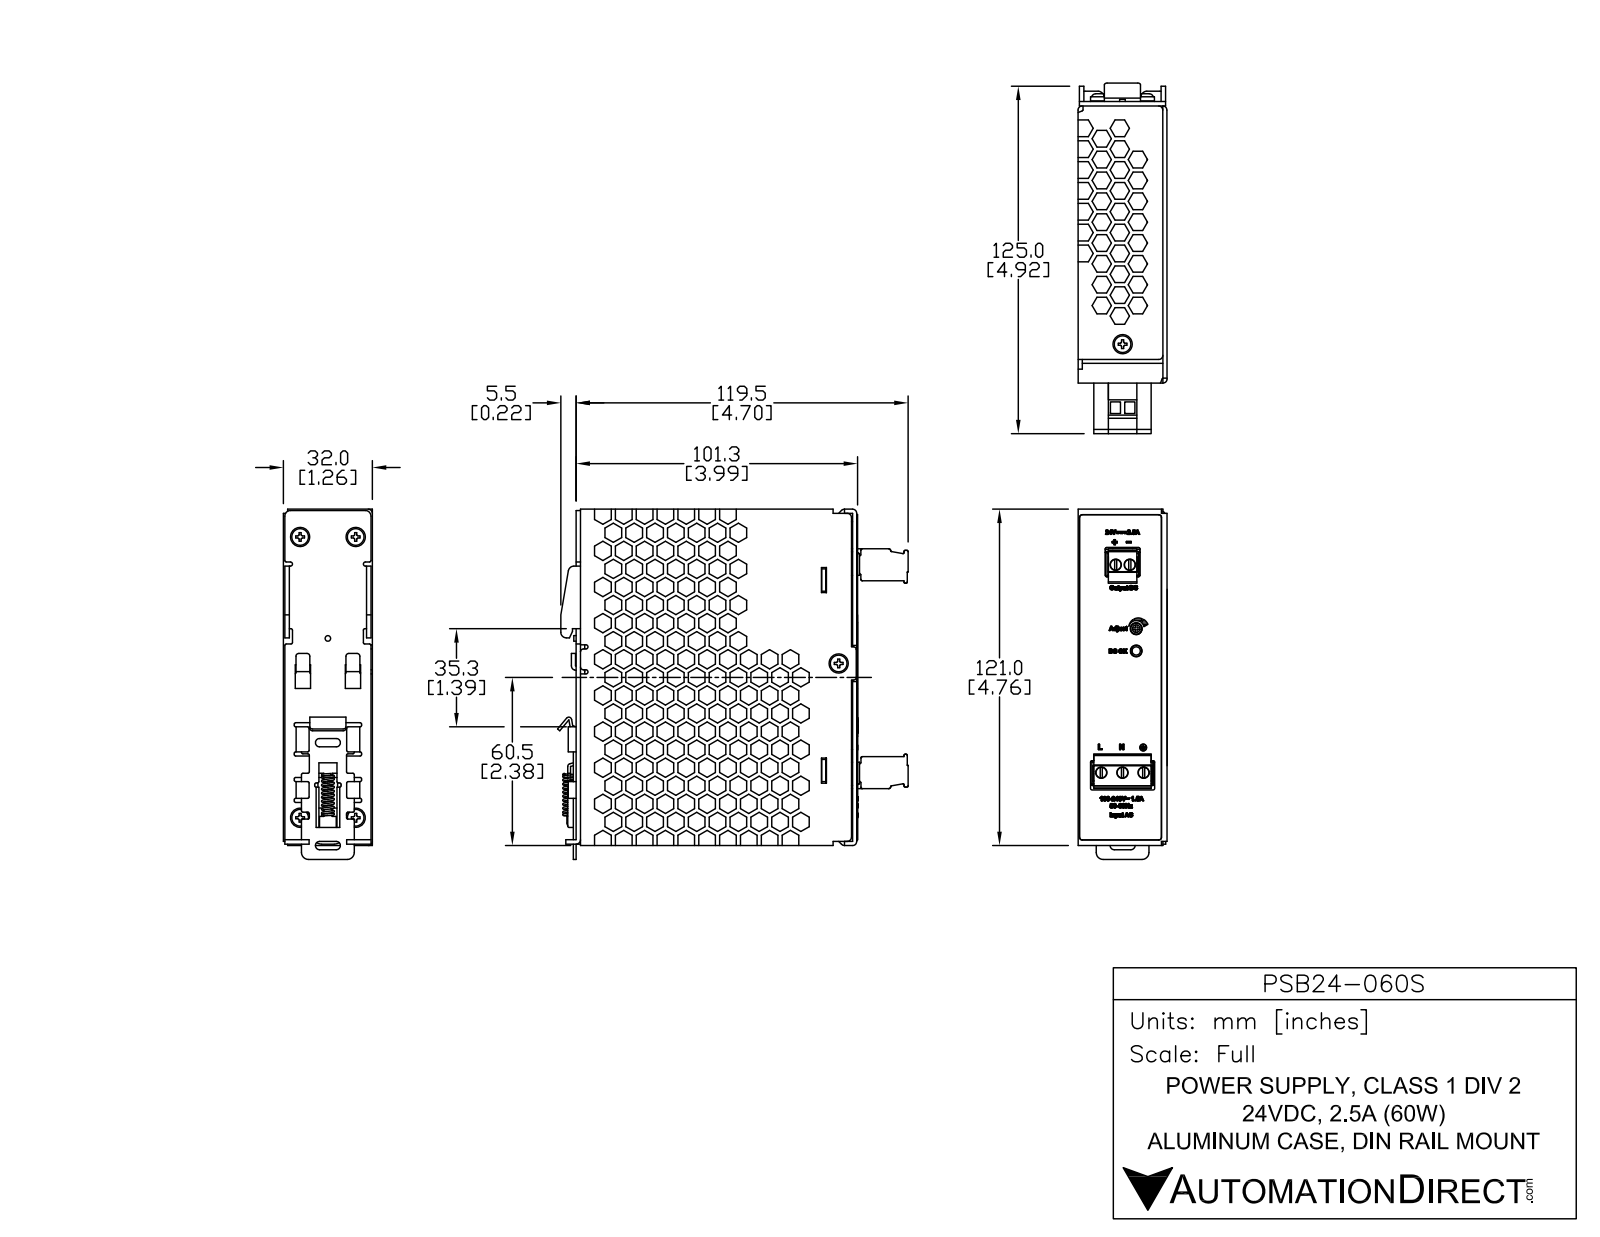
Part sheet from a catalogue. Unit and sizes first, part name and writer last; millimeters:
Units: millimetres
Overall size (bounding box): 126.2 × 126 × 32.1
Round holes (diameter × count): ⌀4 ×7, ⌀3.5 ×6, ⌀4.5 ×6, ⌀3 ×4, ⌀6 ×4, ⌀4.2 ×2, ⌀2 ×1, ⌀2.8 ×1, ⌀3.5 ×1, ⌀4.1 ×1
Round bosses / shafts (diameter × count): ⌀3 ×7, ⌀6.5 ×6, ⌀6 ×6, ⌀0.5 ×3, ⌀0.9 ×2, ⌀2.3 ×1
Partial cylindrical surfaces — rounded edges, fillets, slot ends (radius × count): R0.5 ×117, R1 ×33, R1.5 ×30, R0.1 ×14, R0.8 ×14, R2 ×10, R1.6 ×9, R0.2 ×8
Main face-to-face distances: 1.5, 1.6, 30.5, 5.6, 7.1, 4, 5.5, 24.9, 26.5, 32
Hole centre spacings: 7.6, 20, 37.8, 65.3, 74.8, 79.3, 101, 103
Volume: 80 120 mm³ · Surface area: 128 600 mm²
Bodies: 29 solids, 4511 faces (3184 planar, 535 cylindrical, 792 other)
Part name (STEP PRODUCT): 3103000601; 3202315200_2; 3050252046_1; 346008810000 (+8 more)
STEP written by: SolidWorks 2014 (AUTOMOTIVE_DESIGN)
